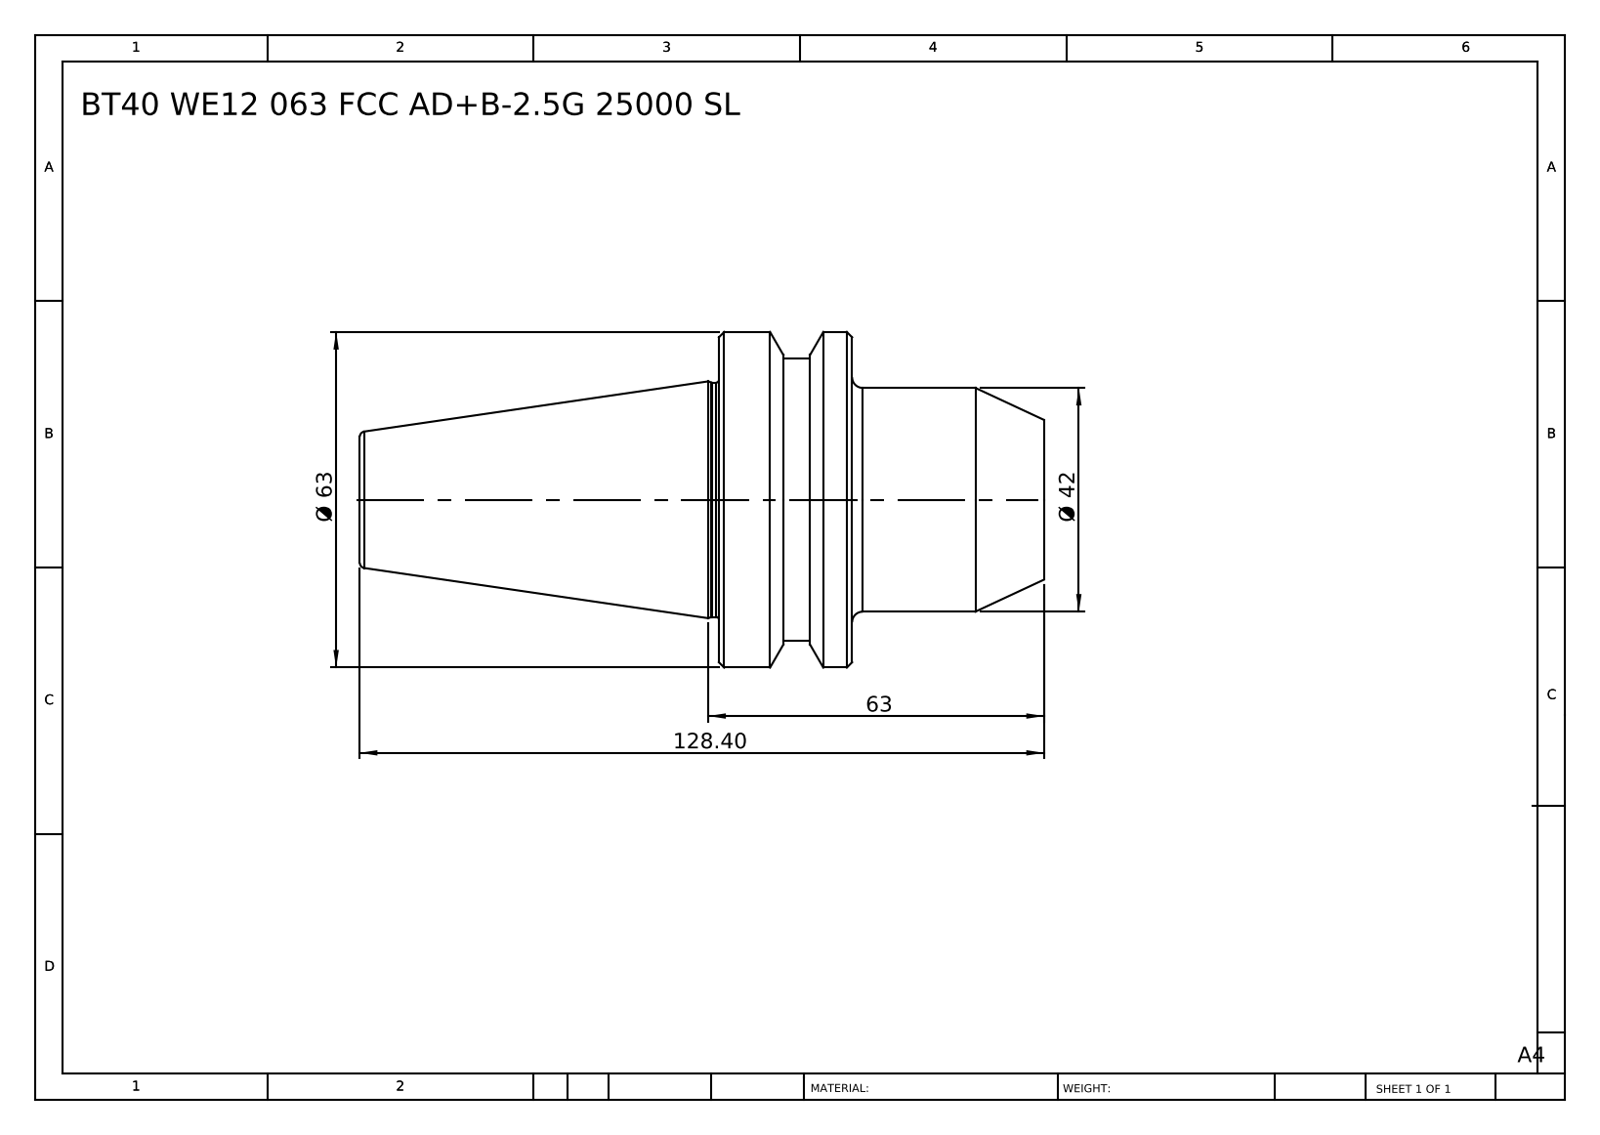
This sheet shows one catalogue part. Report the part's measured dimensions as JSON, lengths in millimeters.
{"part_name": "BT40 WE12 063 AD-6.3G15000 SL", "step_written_by": "SolidWorks 2014 (CONFIG_CONTROL_DESIGN)", "units": "millimeters", "bodies": {"solids": 1, "faces": 38, "planar": 6, "cylindrical": 10, "other": 22}, "overall_size": [128.4, 63, 63], "volume_mm3": 183730, "surface_area_mm2": 22201, "round_bosses_or_shafts": [[63, 1], [53, 1], [44, 1], [42, 1]], "face_to_face_distances": [25, 36, 61, 128.4, 92.4, 67.4, 48.9, 12.9, 12.1, 79.5]}
